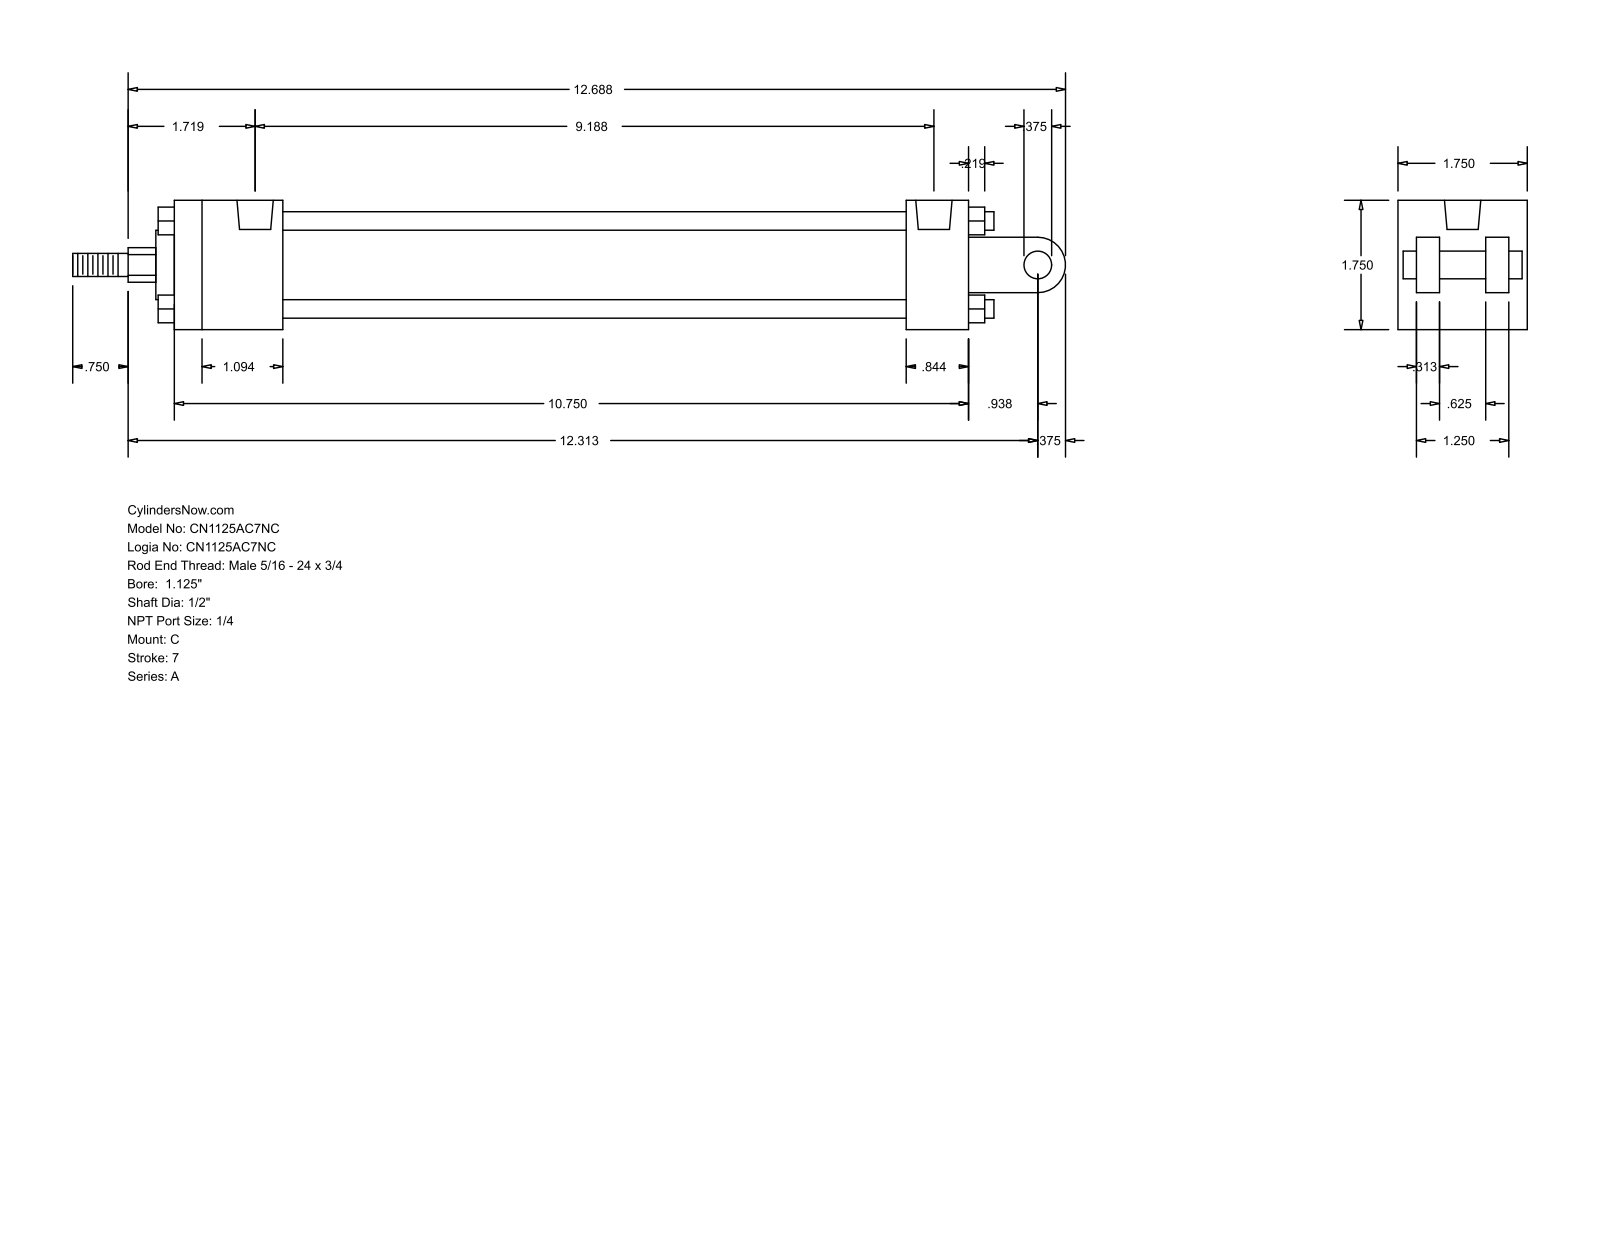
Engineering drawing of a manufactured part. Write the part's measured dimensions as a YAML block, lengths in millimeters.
part_name: "A_C__0112_0.5"
step_written_by: "GSSL Pune (CONFIG_CONTROL_DESIGN)"
units: millimeters
bodies: {solids: 0, faces: 135, planar: 102, cylindrical: 33, other: 0}
overall_size: [341.31, 44.45, 44.45]
round_holes:
  - {diameter: 5.56, count: 4}
  - {diameter: 12.49, count: 2}
round_bosses_or_shafts:
  - {diameter: 6.35, count: 4}
  - {diameter: 31.88, count: 1}
  - {diameter: 23.81, count: 1}
  - {diameter: 12.7, count: 1}
  - {diameter: 9.53, count: 1}
  - {diameter: 7.94, count: 1}
partial_cylinders:
  - {radius: 5.94, count: 1}
  - {radius: 9.53, count: 1}
face_to_face_distances: [44.46, 6.35, 31.76, 14.29, 273.05, 30.17, 251.61, 21.44, 37.3, 214.31]
hole_center_spacings: [230.19, 1.58, 1.59, 231.77, 231.78, 233.36]
